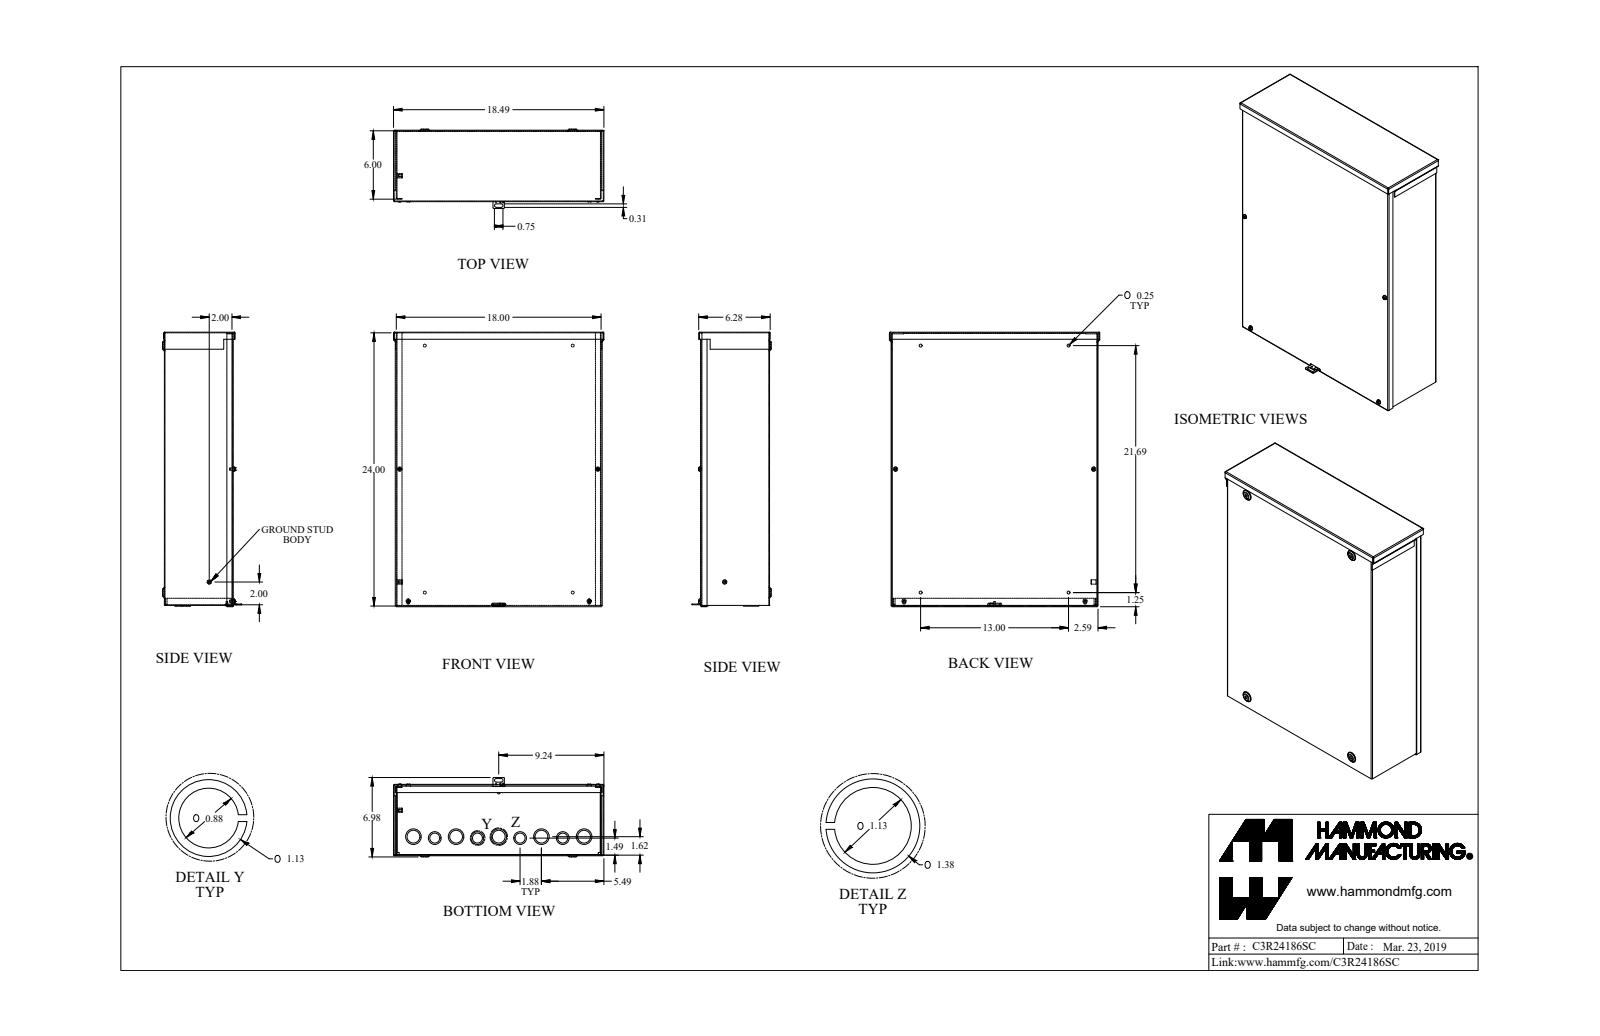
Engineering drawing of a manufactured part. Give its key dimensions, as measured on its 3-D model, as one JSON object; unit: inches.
{"part_name": "C3R24186SC_Default", "step_written_by": "SolidWorks 2019 (CONFIG_CONTROL_DESIGN)", "units": "inches", "bodies": {"solids": 11, "faces": 457, "planar": 238, "cylindrical": 133, "other": 86}, "overall_size": [24.12, 18.489, 6.977], "volume_in3": 85.51, "surface_area_in2": 3013, "round_holes": [[0.17, 4], [0.25, 4], [1.125, 3], [0.875, 2], [0.875, 2], [1.125, 2], [0.125, 1], [0.137, 1], [0.156, 1]], "round_bosses_or_shafts": [[1.125, 4], [0.19, 4], [1.375, 3], [0.375, 3], [1.375, 2], [0.375, 2], [0.125, 1]], "partial_cylinders_radius": [[0.029, 21], [0.086, 21], [0.109, 8], [0.125, 8], [0.156, 2]], "face_to_face_distances": [0.057, 6, 5.943, 6.057, 17.943, 0.057, 18, 17.886, 23.886, 23.943], "hole_center_spacings": [3.75, 1.879, 1.88, 5.627, 7.5, 11.069, 18.679, 9.376]}
